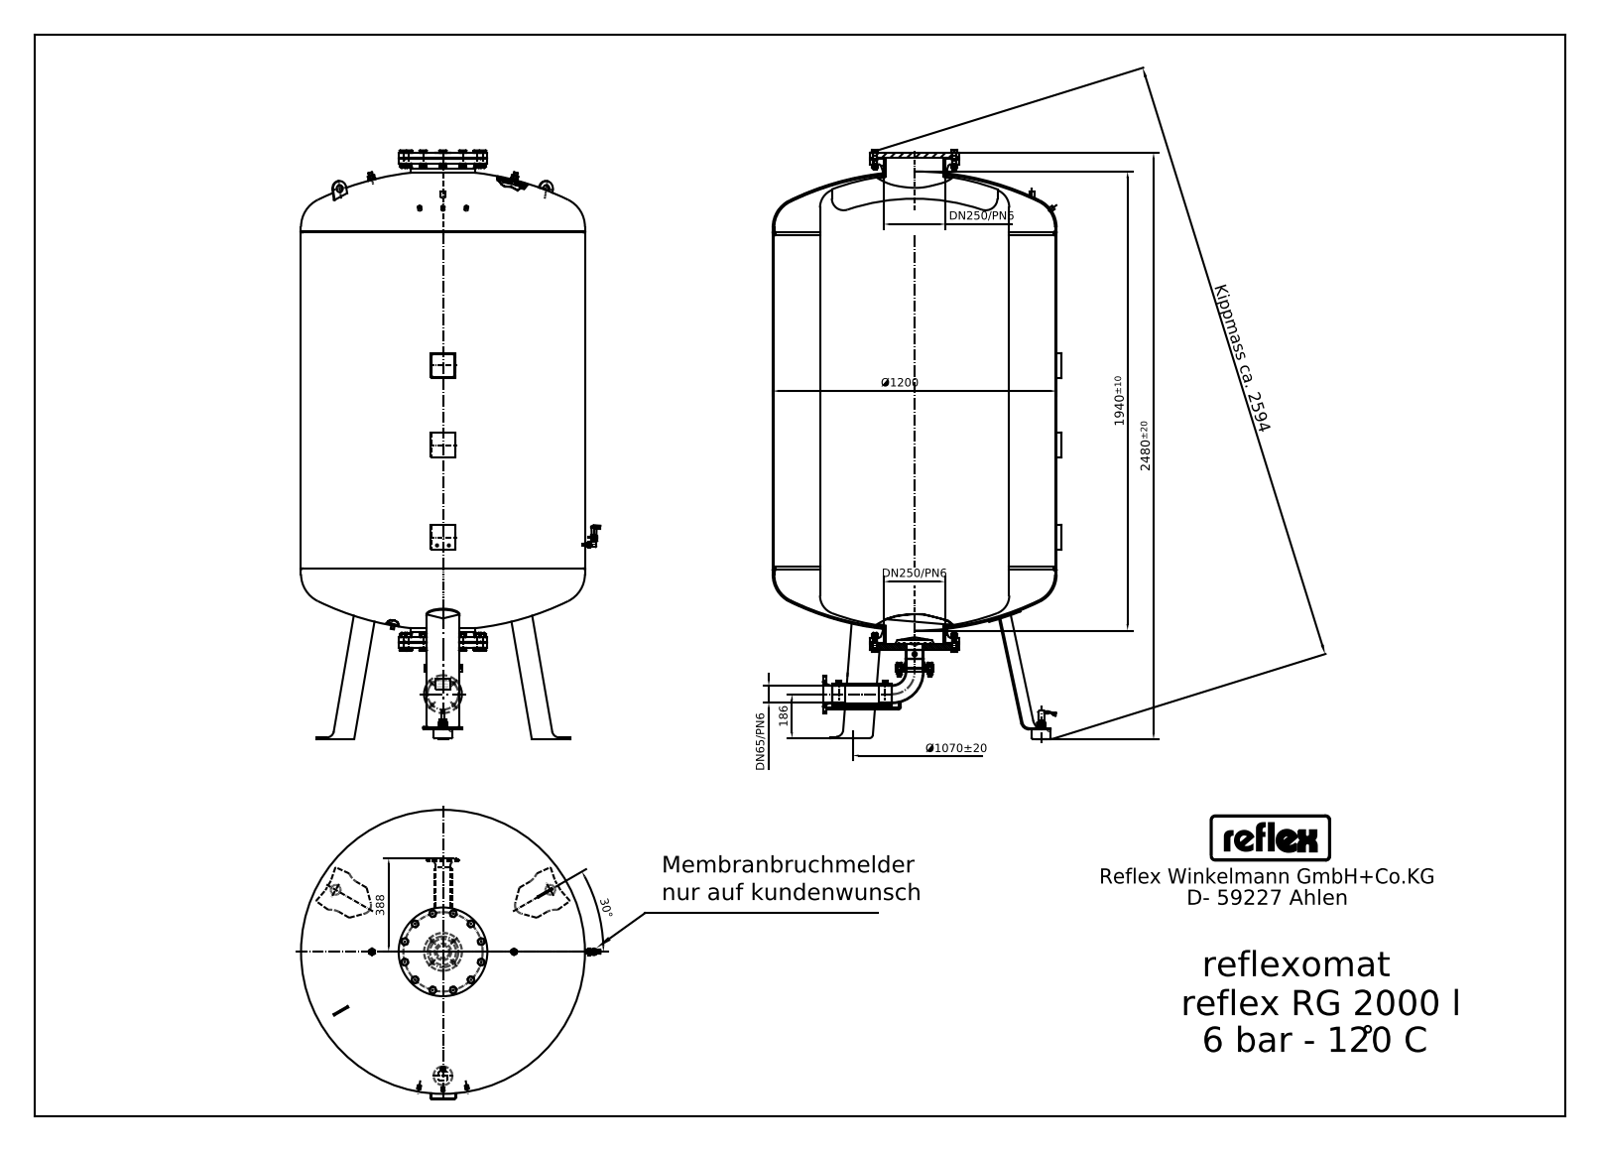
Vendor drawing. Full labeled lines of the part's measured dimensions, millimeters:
STEP written by: Mechanical Desktop 2009 (CONFIG_CONTROL_DESIGN)
Units: millimetres
Bodies: 33 solids, 1189 faces (677 planar, 280 cylindrical, 232 other)
Overall size (bounding box): 2490 × 1266 × 1220
Volume: 2 025 000 000 mm³ · Surface area: 15 300 000 mm²
Round holes (diameter × count): ⌀9 ×2, ⌀11.45 ×2, ⌀3.5 ×1, ⌀8 ×1, ⌀14.95 ×1, ⌀30 ×1, ⌀260.4 ×1
Round bosses / shafts (diameter × count): ⌀16 ×12, ⌀12 ×4, ⌀21.3 ×3, ⌀18.5 ×3, ⌀76.1 ×2, ⌀28 ×2, ⌀20 ×2, ⌀10 ×2
Partial cylindrical surfaces — rounded edges, fillets, slot ends (radius × count): R25 ×18, R2 ×10, R1 ×5, R8.44 ×4, R3.38 ×3, R6 ×3, R3 ×2, R5.76 ×2
Main face-to-face distances: 1430, 22, 2075, 27, 2048, 335, 1743, 313, 2097, 1765
Hole centre spacings: 720.43, 50, 495, 619.5, 792.97, 1574.76, 1590.55, 2276.99
